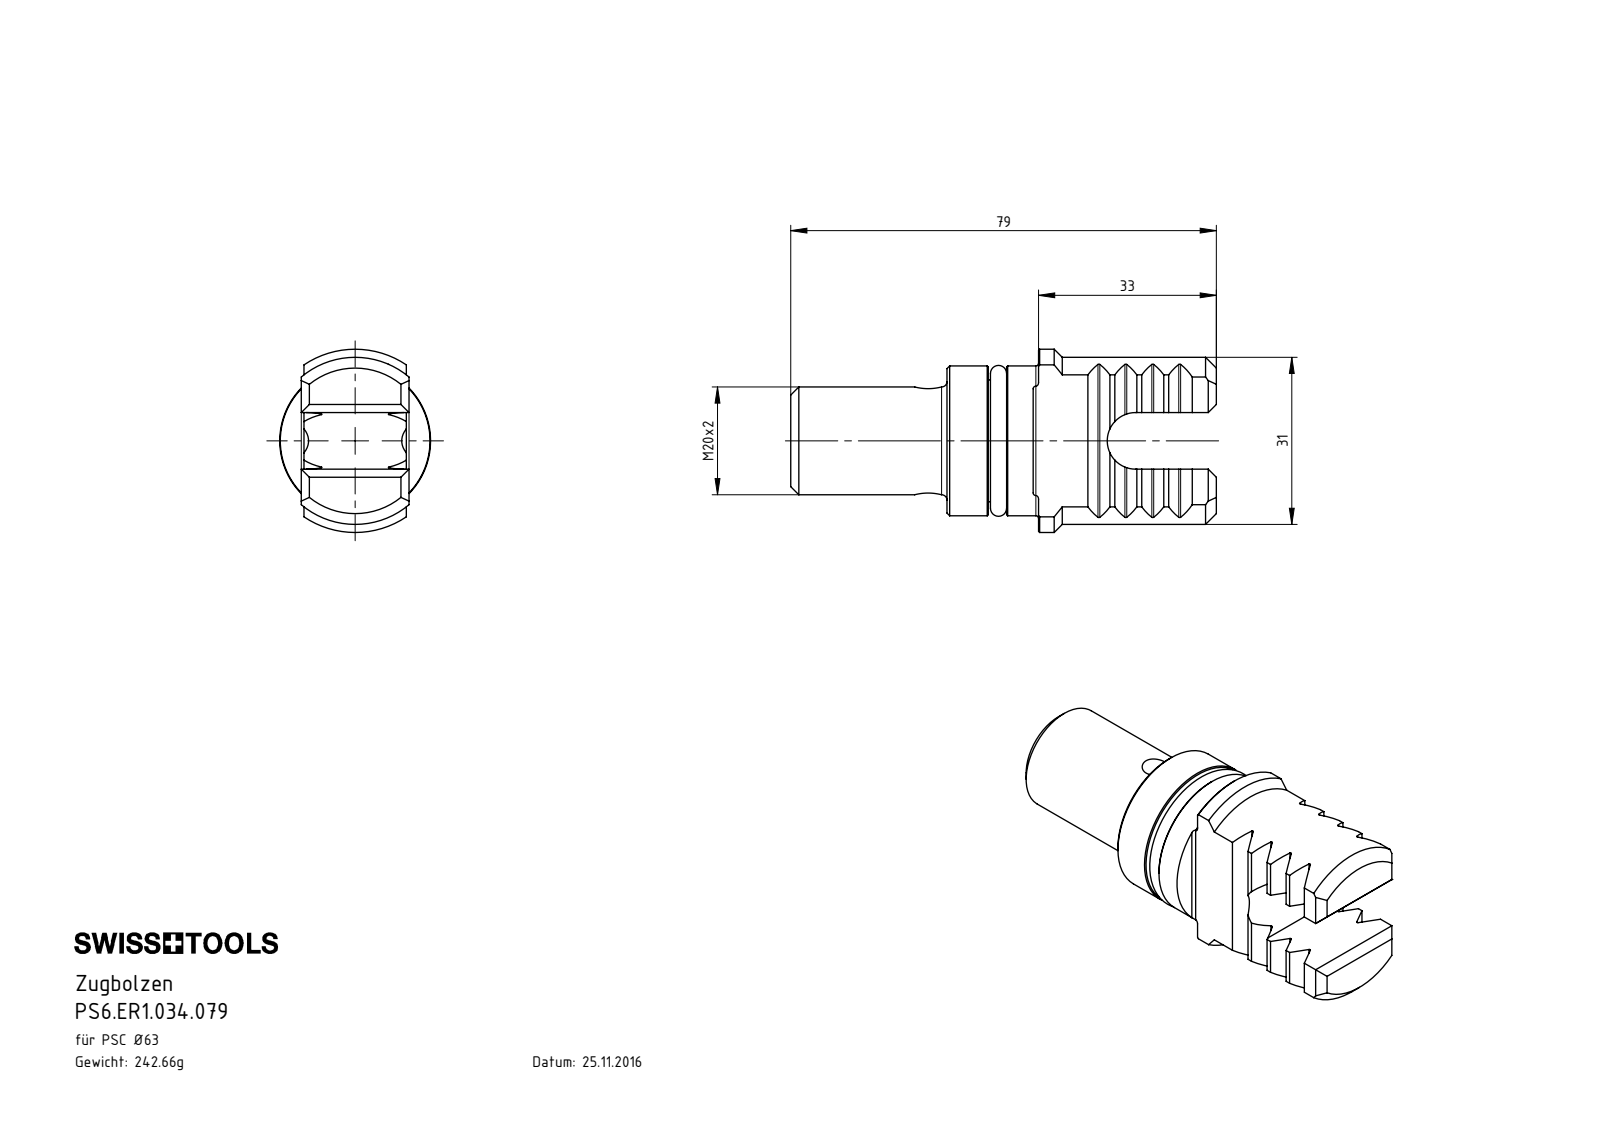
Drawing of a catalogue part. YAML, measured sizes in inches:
part_name: "DIN 3771 - 22x3; PS6-ER1.034.079_B; PS6-ER1.034.079"
step_written_by: "SolidWorks 2017 (AUTOMOTIVE_DESIGN)"
units: inches
bodies: {solids: 2, faces: 131, planar: 64, cylindrical: 37, other: 30}
overall_size: [3.11, 1.339, 1.102]
volume: 1.916
surface_area: 15.46
round_holes:
  - {diameter: 0.197, count: 1}
  - {diameter: 0.236, count: 1}
round_bosses_or_shafts:
  - {diameter: 1.094, count: 1}
  - {diameter: 0.89, count: 1}
  - {diameter: 0.787, count: 1}
partial_cylinders:
  - {radius: 0.008, count: 8}
  - {radius: 0.02, count: 2}
  - {radius: 0.207, count: 1}
  - {radius: 0.61, count: 1}
  - {radius: 0.669, count: 1}
face_to_face_distances: [0.17, 0.235, 0.341, 0.405, 0.064, 0.748, 0.511, 0.106, 0.576, 0.413]
